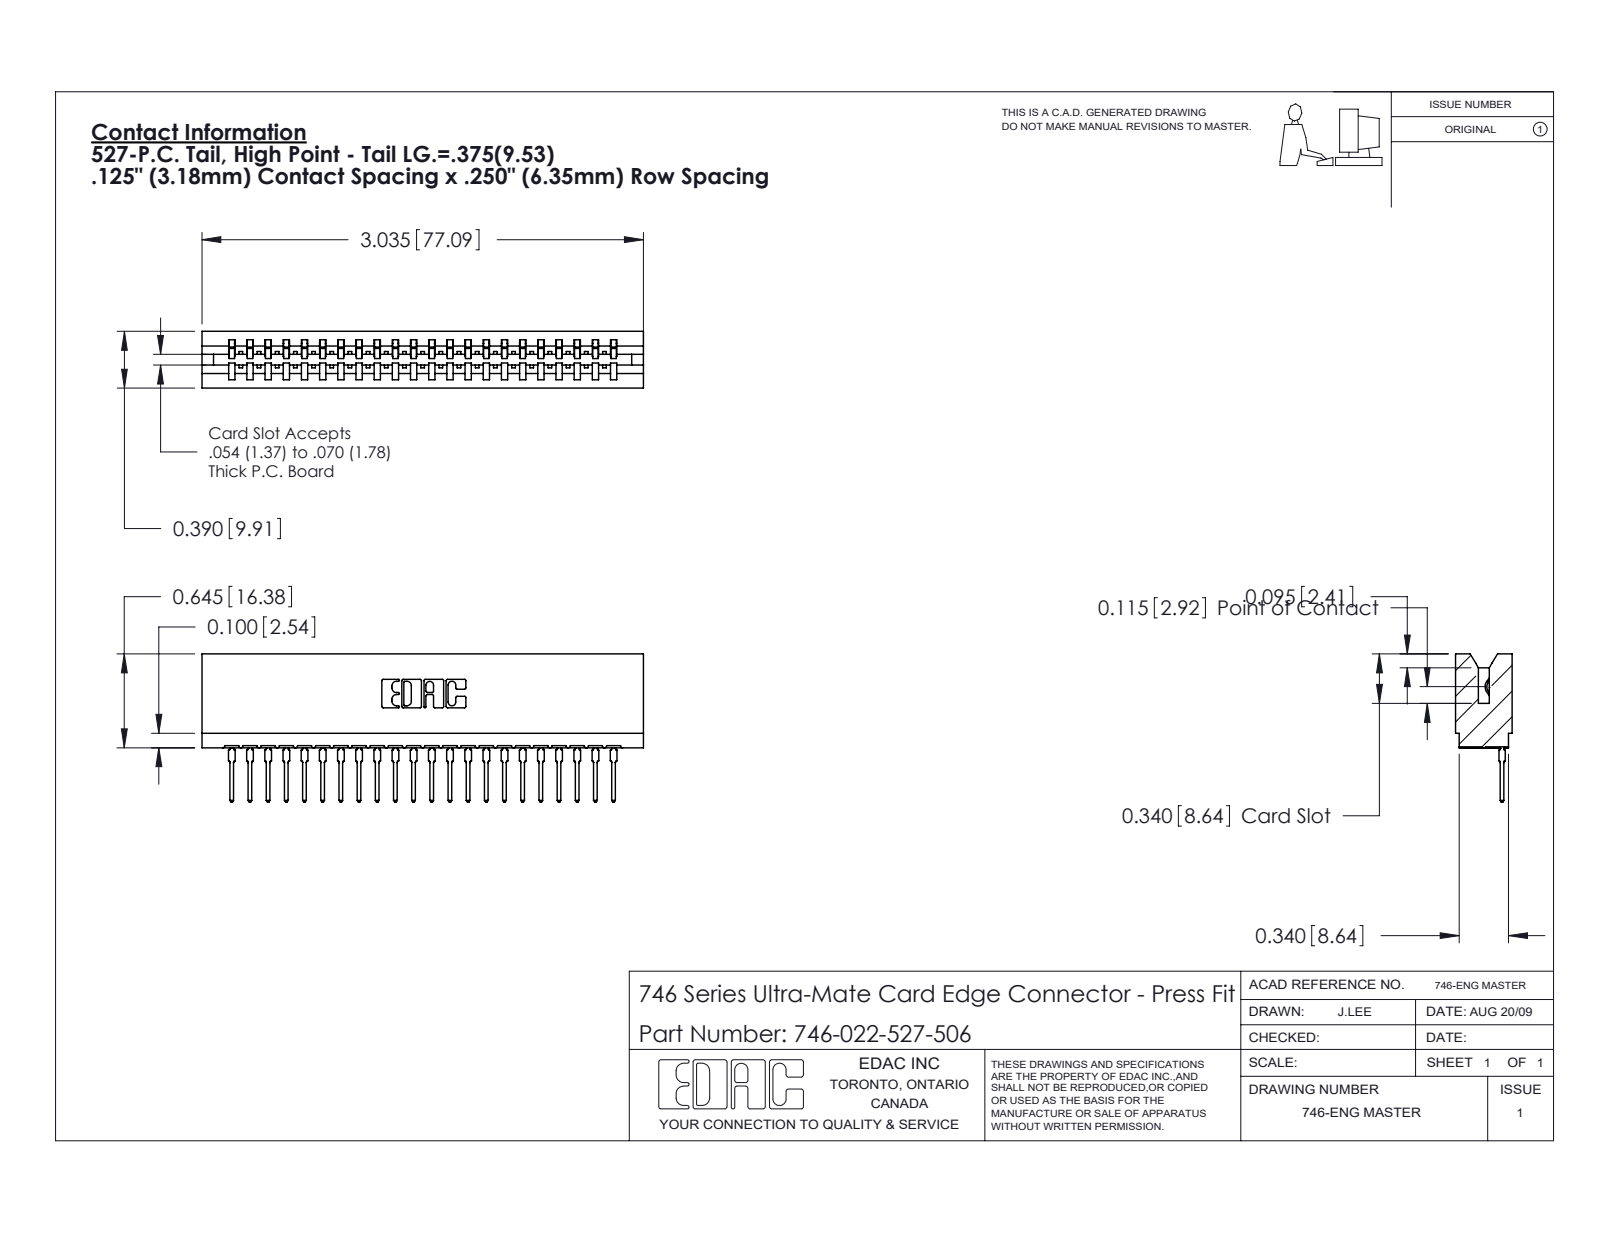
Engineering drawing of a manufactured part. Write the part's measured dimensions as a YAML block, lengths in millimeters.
part_name: "746 Part_.340 Slot Depth - 06; 746-022-527-506; 746-292-001_527"
step_written_by: "SolidWorks 2020 (CONFIG_CONTROL_DESIGN)"
units: millimeters
bodies: {solids: 23, faces: 2474, planar: 1442, cylindrical: 460, other: 572}
overall_size: [77.1, 25.9, 9.9]
volume: 8770
surface_area: 11660
partial_cylinders:
  - {radius: 0.5, count: 44}
  - {radius: 0.4, count: 23}
  - {radius: 0.3, count: 22}
  - {radius: 0.2, count: 6}
  - {radius: 0.8, count: 6}
  - {radius: 0.1, count: 4}
  - {radius: 0.3, count: 4}
  - {radius: 0.7, count: 3}
face_to_face_distances: [6.4, 1.4, 8.5, 9.9, 12.7, 0.6, 7.8, 1.1, 3.2, 7.4]
